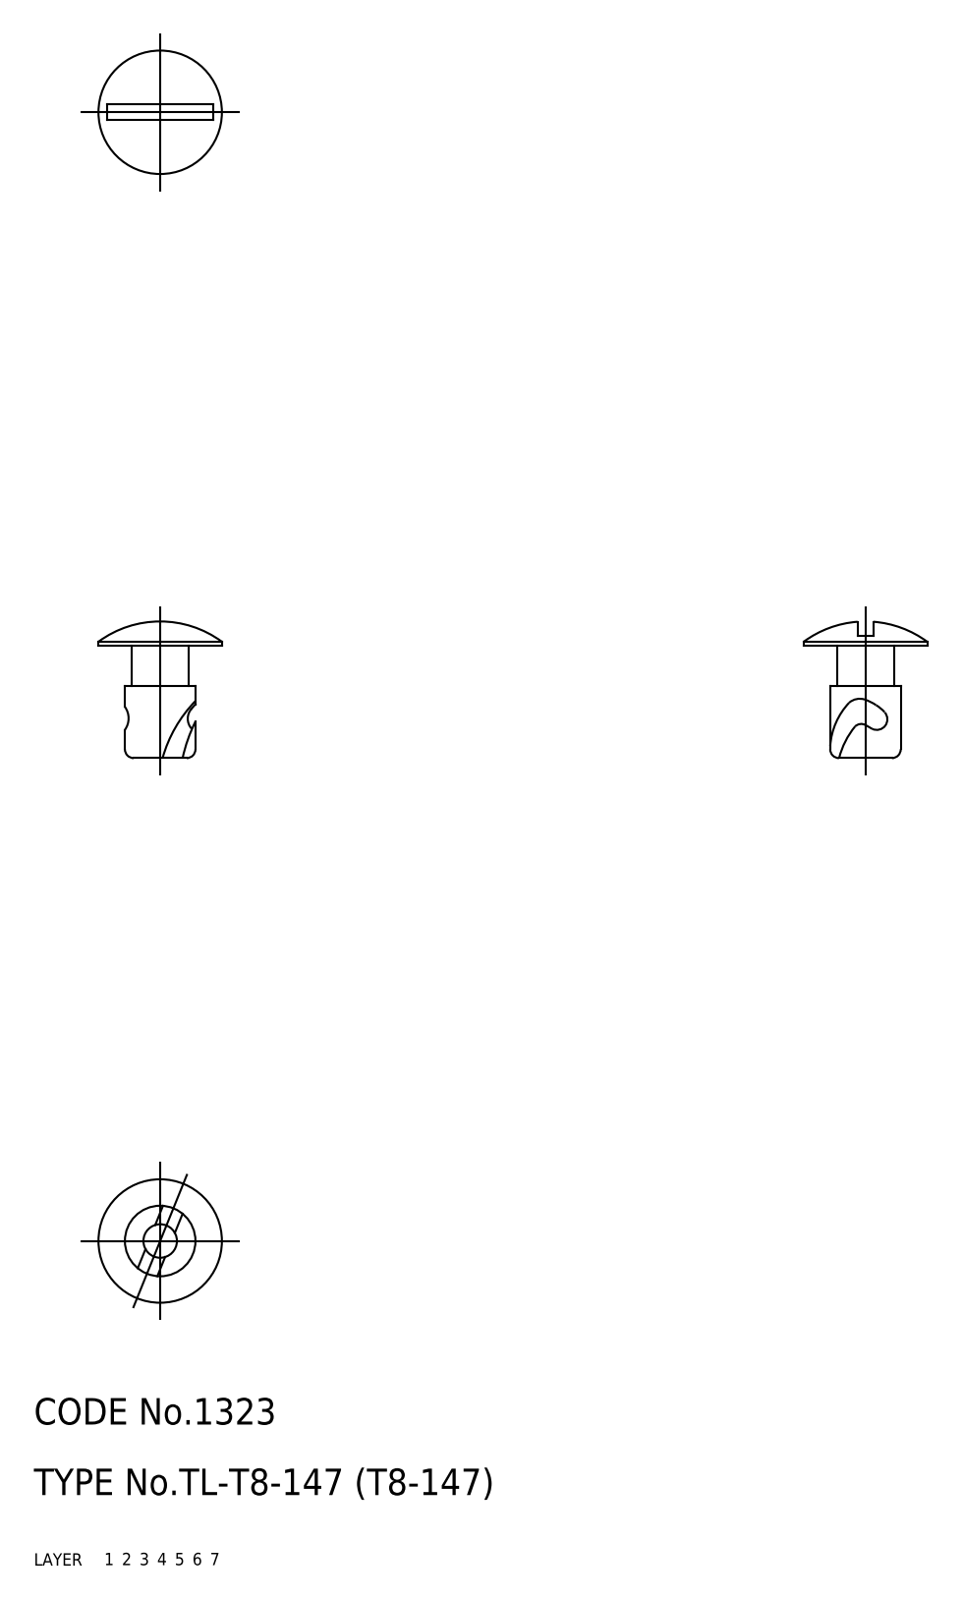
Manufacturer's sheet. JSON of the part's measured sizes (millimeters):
{"part_name": "67113747", "step_written_by": "CADfix (AUTOMOTIVE_DESIGN)", "units": "millimeters", "bodies": {"solids": 1, "faces": 35, "planar": 0, "cylindrical": 0, "other": 35}, "overall_size": [15.47, 14, 14], "volume_mm3": 624, "surface_area_mm2": 775}
